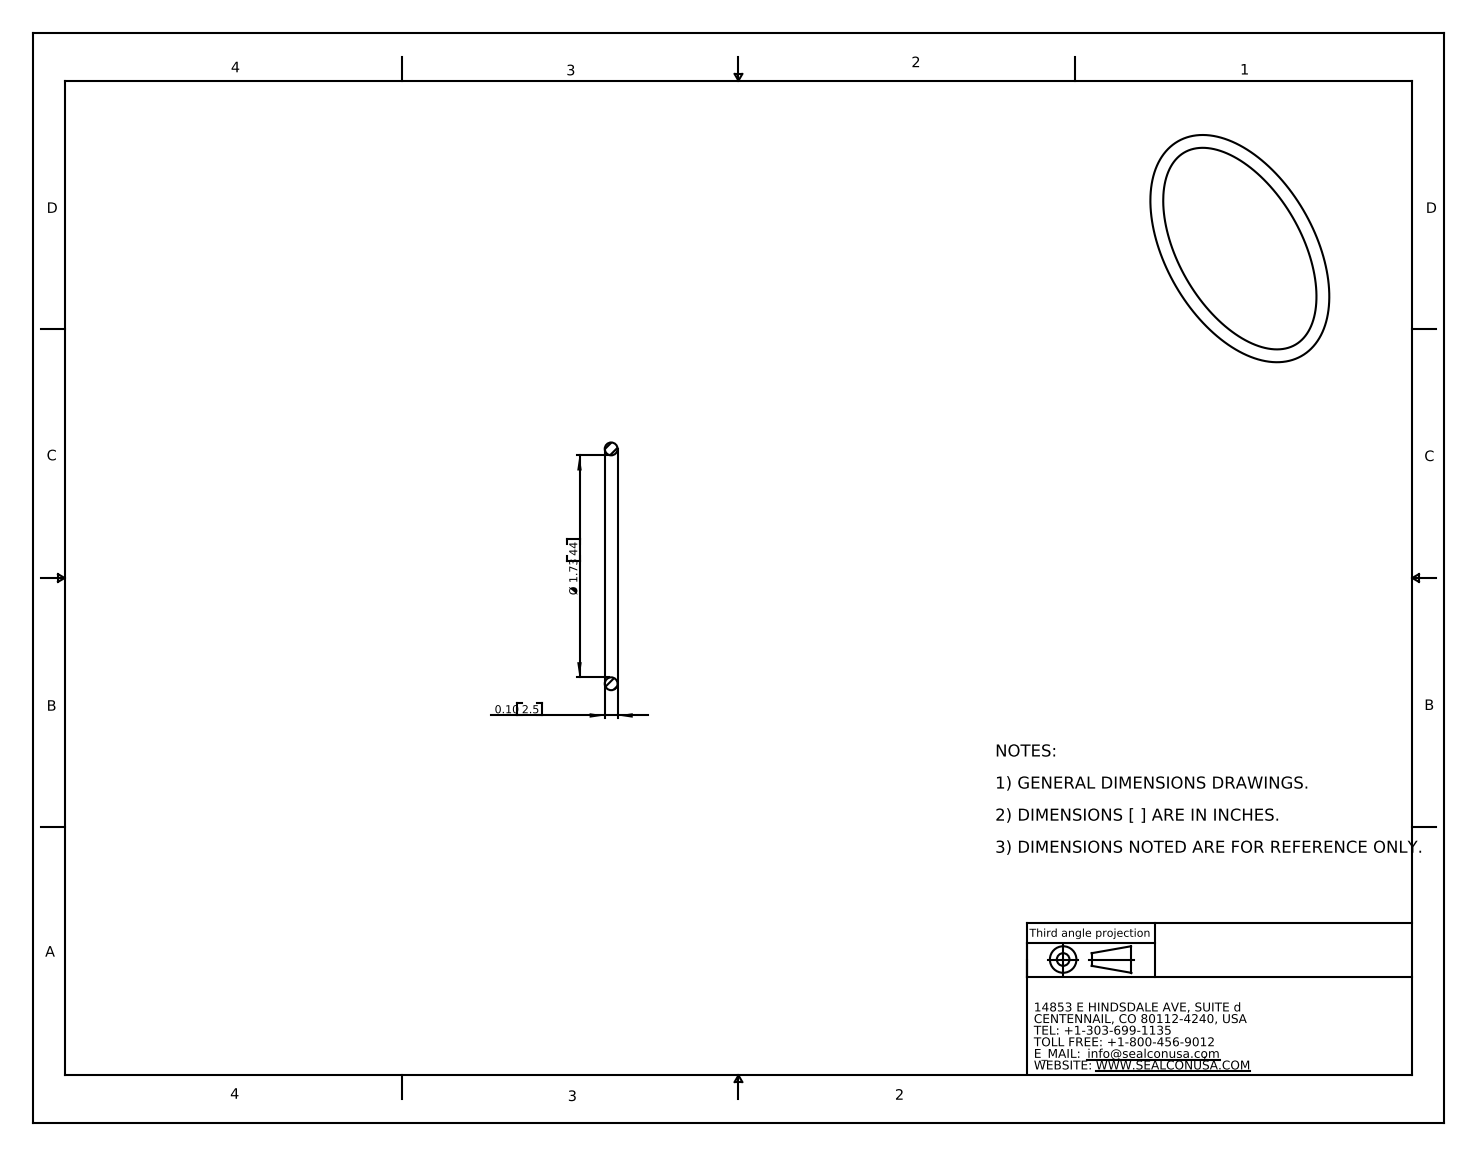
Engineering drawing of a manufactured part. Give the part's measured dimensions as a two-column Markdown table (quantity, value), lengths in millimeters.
| quantity | value |
| --- | --- |
| part name | OR-64-VT |
| STEP written by | SolidWorks 2007 (CONFIG_CONTROL_DESIGN) |
| units | millimeters |
| bodies | 1 solid, 4 faces (0 planar, 0 cylindrical, 4 other) |
| overall size | 49 × 49 × 2.5 |
| volume | 740 mm³ |
| surface area | 1 165 mm² |
